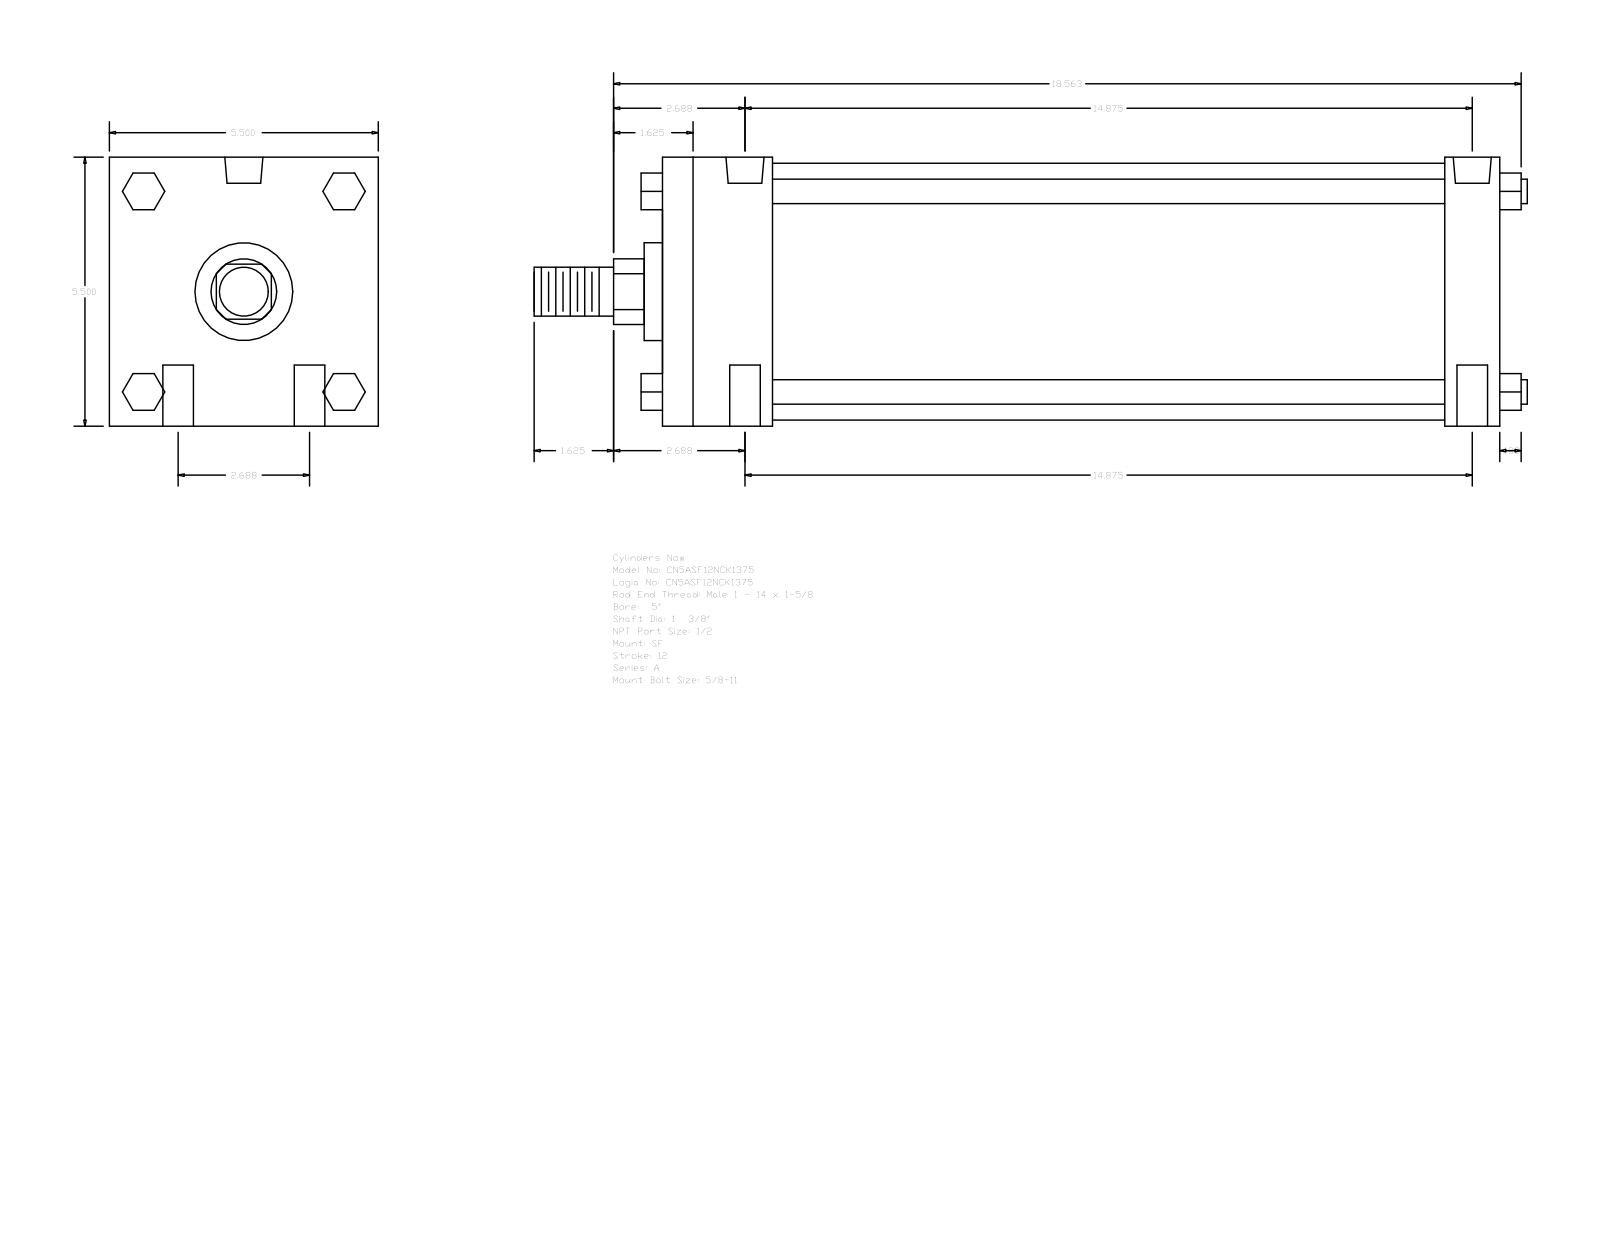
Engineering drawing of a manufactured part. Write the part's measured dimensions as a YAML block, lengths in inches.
part_name: "A_SF__0500_1.375"
step_written_by: "GSSL Pune (CONFIG_CONTROL_DESIGN)"
units: inches
bodies: {solids: 0, faces: 124, planar: 94, cylindrical: 30, other: 0}
overall_size: [20.313, 5.5, 5.5]
round_holes:
  - {diameter: 0.625, count: 4}
  - {diameter: 0.344, count: 2}
  - {diameter: 0.778, count: 2}
round_bosses_or_shafts:
  - {diameter: 0.5, count: 4}
  - {diameter: 5.25, count: 1}
  - {diameter: 2, count: 1}
  - {diameter: 1.375, count: 1}
  - {diameter: 1, count: 1}
partial_cylinders:
  - {radius: 0.672, count: 1}
face_to_face_distances: [5.5, 17.125, 2.25, 1.125, 16, 13.75, 14.875, 0.75, 2.05, 3.55]
hole_center_spacings: [1.344, 14.936, 14.875, 2.687, 15.116, 14.687]
